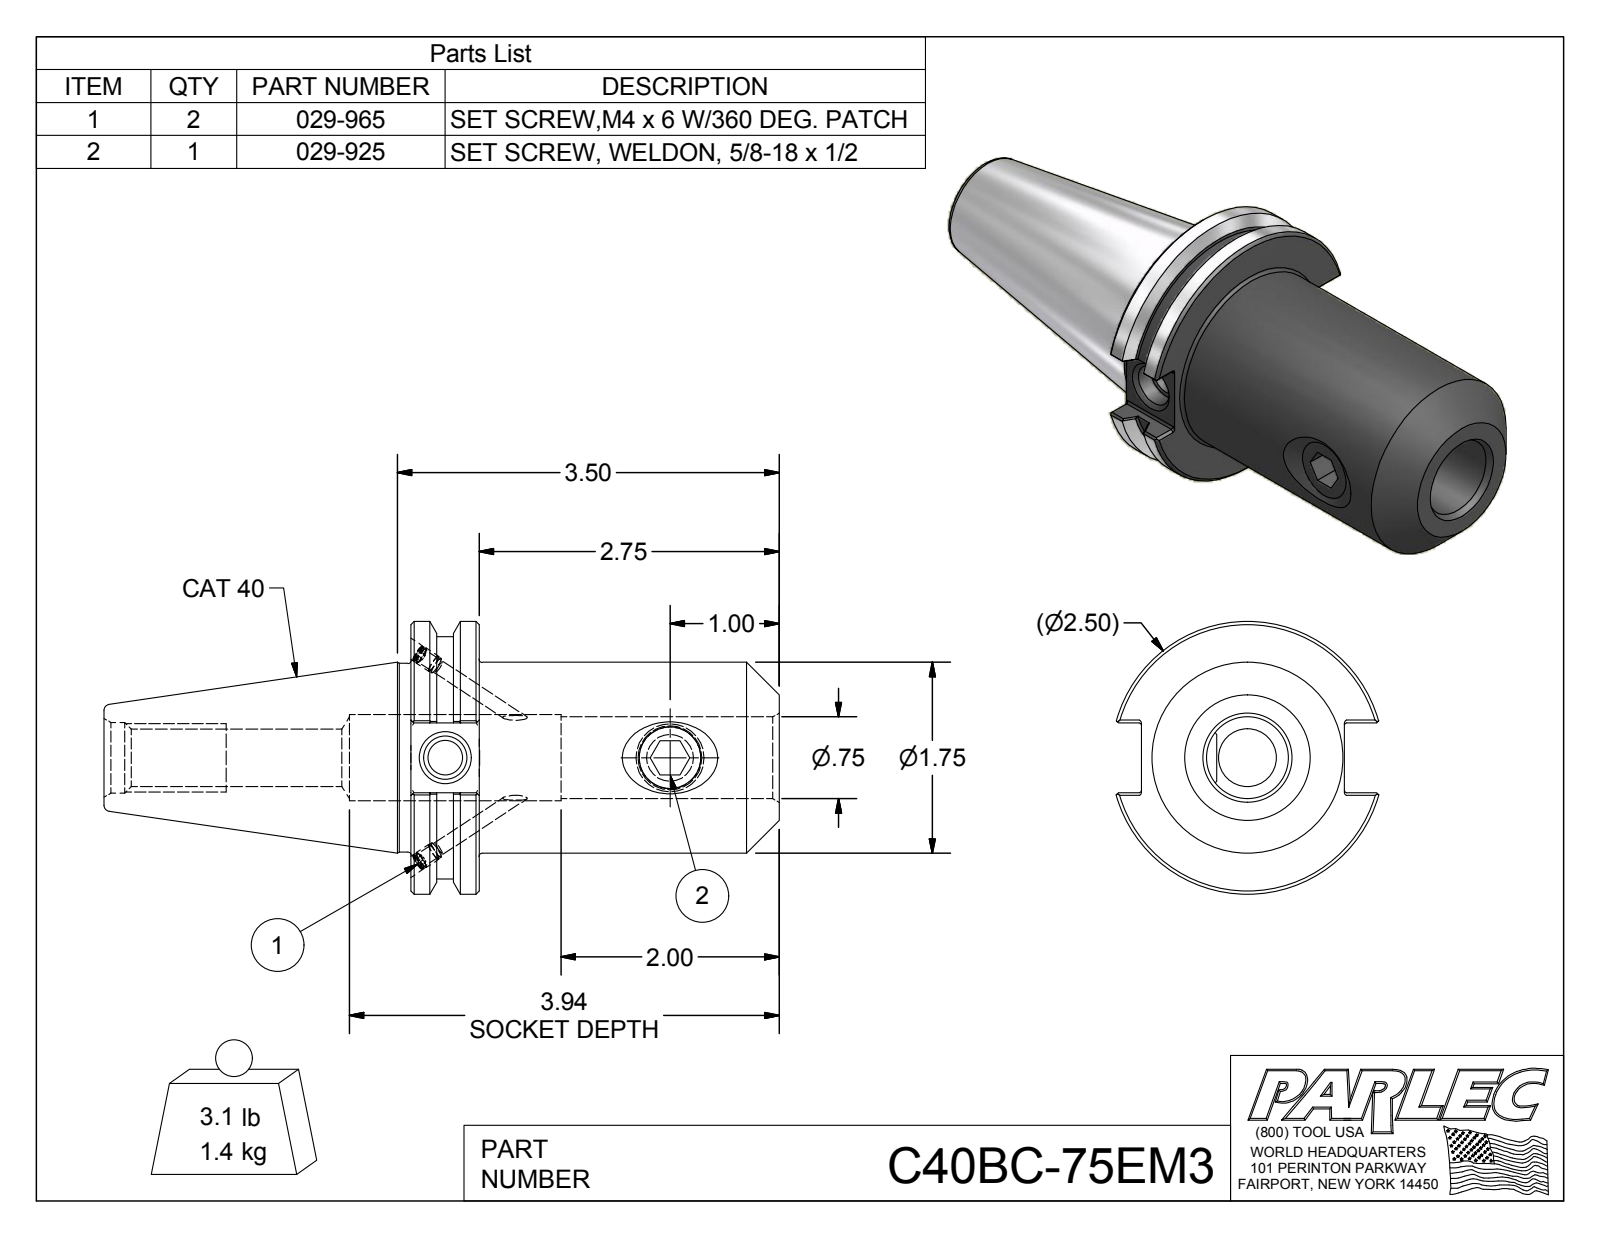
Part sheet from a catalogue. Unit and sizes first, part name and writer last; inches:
Units: inches
Overall size (bounding box): 6.187 × 2.5 × 2.406
Round holes (diameter × count): ⌀0.13 ×2, ⌀0.161 ×2, ⌀0.315 ×1, ⌀0.399 ×1, ⌀0.527 ×1, ⌀0.565 ×1, ⌀0.648 ×1, ⌀0.75 ×1, ⌀0.79 ×1
Round bosses / shafts (diameter × count): ⌀0.165 ×2, ⌀0.157 ×2, ⌀2.5 ×1, ⌀2.219 ×1, ⌀1.75 ×1, ⌀1.73 ×1, ⌀0.625 ×1
Partial cylindrical surfaces — rounded edges, fillets, slot ends (radius × count): R0.02 ×12
Main face-to-face distances: 0.625, 3.375, 2.75, 0.387, 0.64, 0.315, 1.86, 2.812, 3.437, 6.187
Hole centre spacings: 2.06
Volume: 10.89 in³ · Surface area: 56.2 in²
Bodies: 4 solids, 139 faces (64 planar, 38 cylindrical, 37 other)
Part name (STEP PRODUCT): C40BC-75EM3; C40BC-75EM3-1; 029-925; 029-965
STEP written by: Autodesk Inventor 2012 (AUTOMOTIVE_DESIGN)
